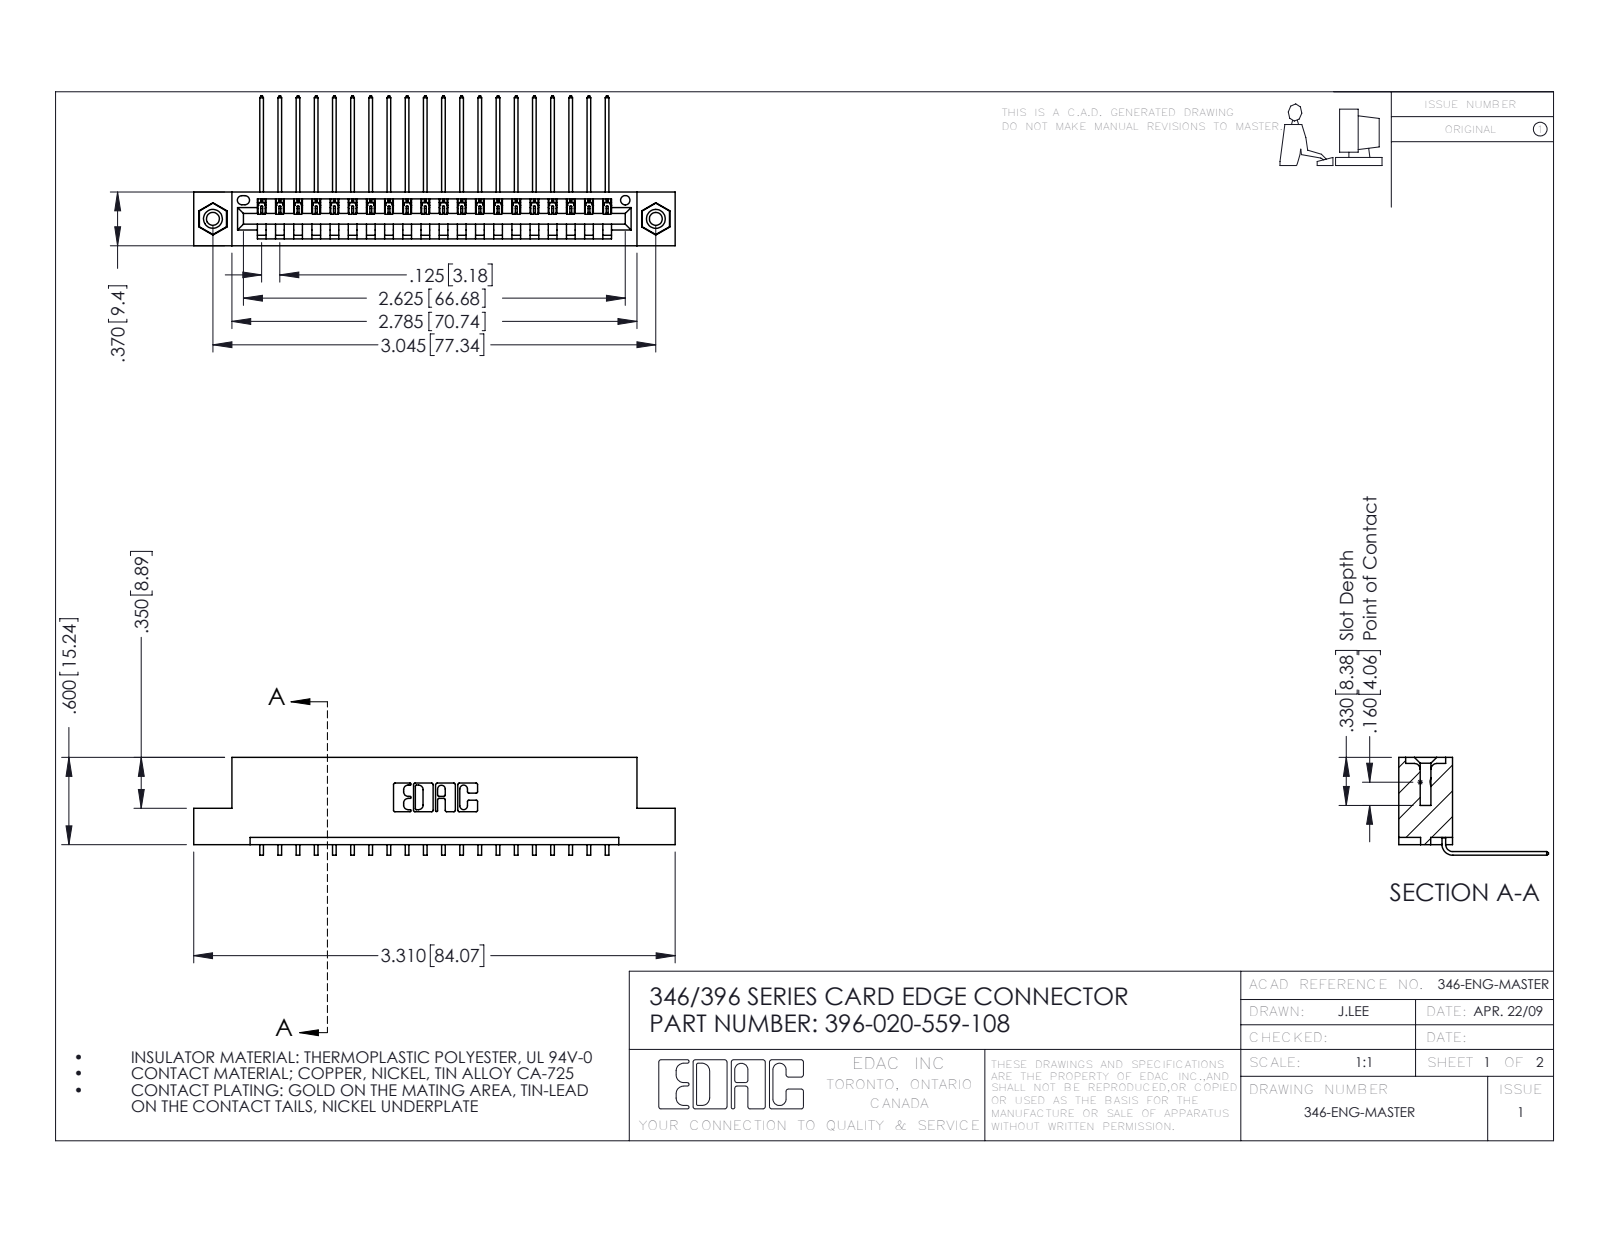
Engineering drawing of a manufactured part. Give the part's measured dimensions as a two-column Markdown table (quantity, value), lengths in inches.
| quantity | value |
| --- | --- |
| part name | 346 Part_Flush Mounting Lugs - 0.156 Dia-TI; 345-250-001_345-250-003-102; 345-292-001_558 559 Tail - 1; 396-020-559-108 |
| STEP written by | SolidWorks 2016 (CONFIG_CONTROL_DESIGN) |
| units | inches |
| bodies | 23 solids, 1382 faces (948 planar, 418 cylindrical, 16 other) |
| overall size | 3.31 × 1.03 × 0.673 |
| volume | 0.486 in³ |
| surface area | 15.7 in² |
| round holes (diameter × count) | 0.089 × 2, 0.125 × 2, 0.156 × 2, 0.064 × 1 |
| round bosses / shafts (diameter × count) | 0.155 × 2 |
| partial cylindrical surfaces (radius × count) | 0.006 × 40, 0.01 × 22, 0.007 × 6, 0.031 × 6, 0.026 × 3, 0.031 × 2, 0.04 × 2, 0.014 × 1 |
| main face-to-face distances | 0.048, 0.322, 0.37, 0.25, 0.072, 0.025, 0.298, 0.148, 0.222, 0.1 |
| hole center spacings | 0.246, 2.837, 3.045 |
